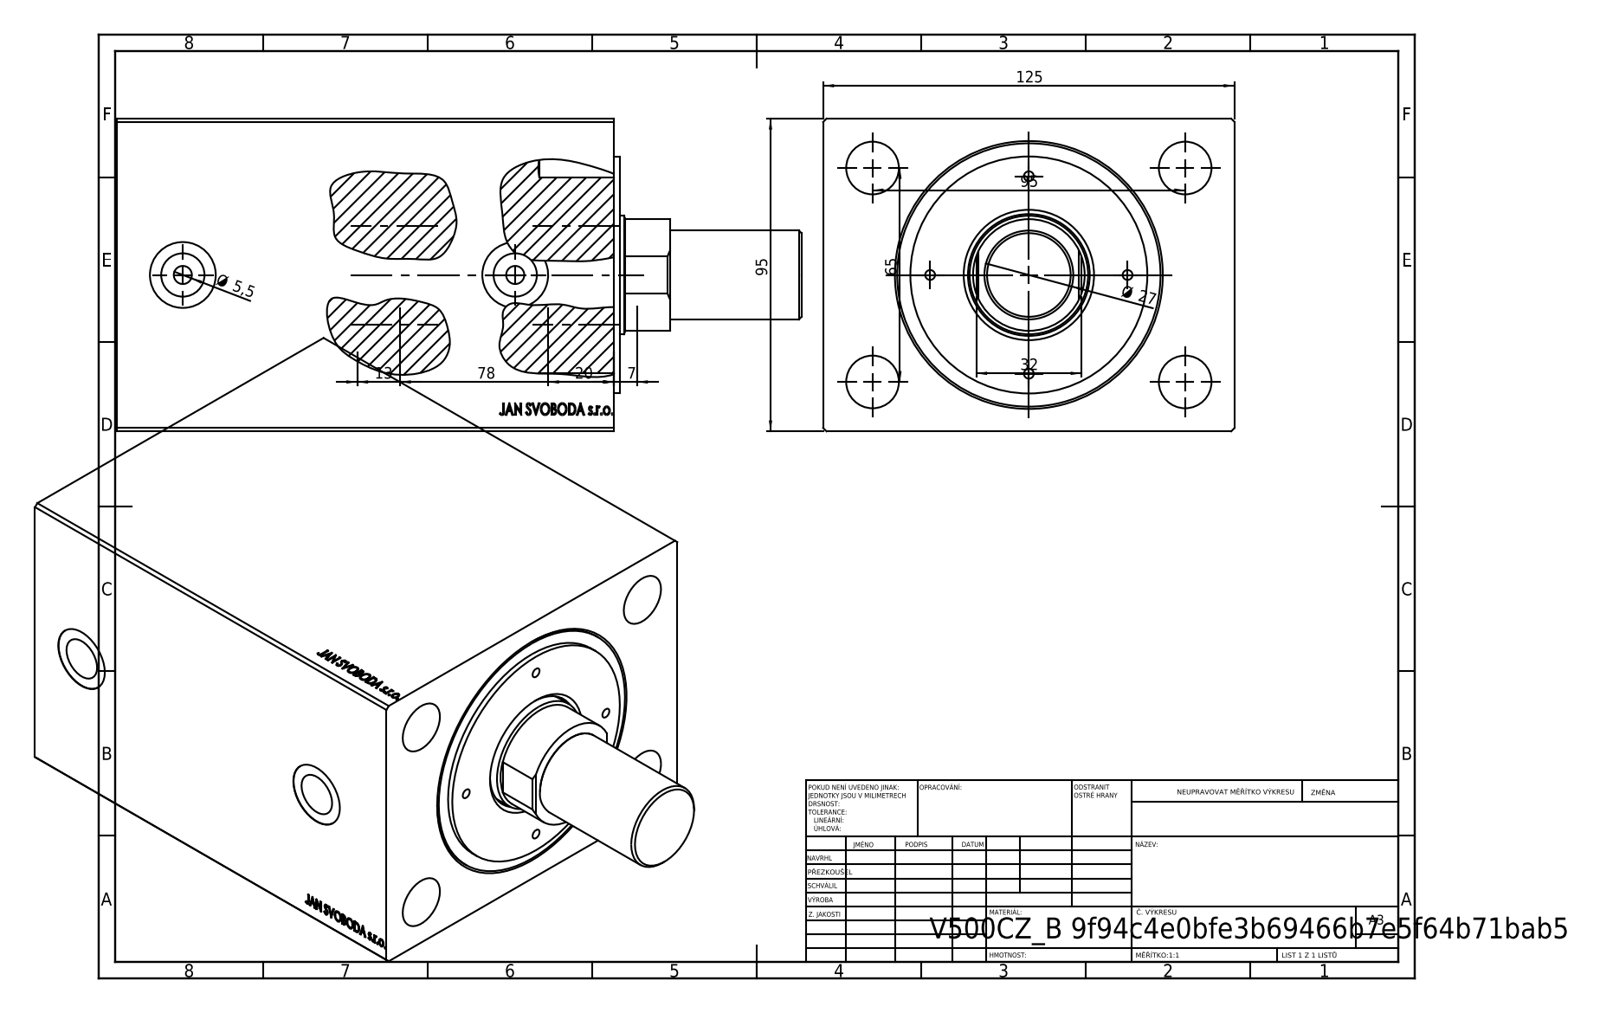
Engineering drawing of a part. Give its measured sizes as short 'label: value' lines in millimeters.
name: V500CZ_vnitrni_cast_vysunovaci; V500CZ; V500CZ_SMALL_MALE_METRIC
written by: SolidWorks 2019 (CONFIG_CONTROL_DESIGN)
unit: mm
bodies: 4 solids, 876 faces (403 planar, 61 cylindrical, 412 other)
size: 208 × 125 × 95
volume: 1 655 000 mm³; area: 159 422 mm²
holes: 4× ⌀3, 4× ⌀16, 2× ⌀5.5, 2× ⌀13.16, 2× ⌀20, 1× ⌀27, 1× ⌀36, 1× ⌀37, 1× ⌀63, 1× ⌀80
bosses: 1× ⌀72
rounds: 1× R16.96
face distances: 95, 125, 151, 56, 85, 10, 141, 1.8, 11.8, 96.8
hole spacings: 30, 36.91, 42.43, 47.57, 57.55, 78.5, 84.04, 60
